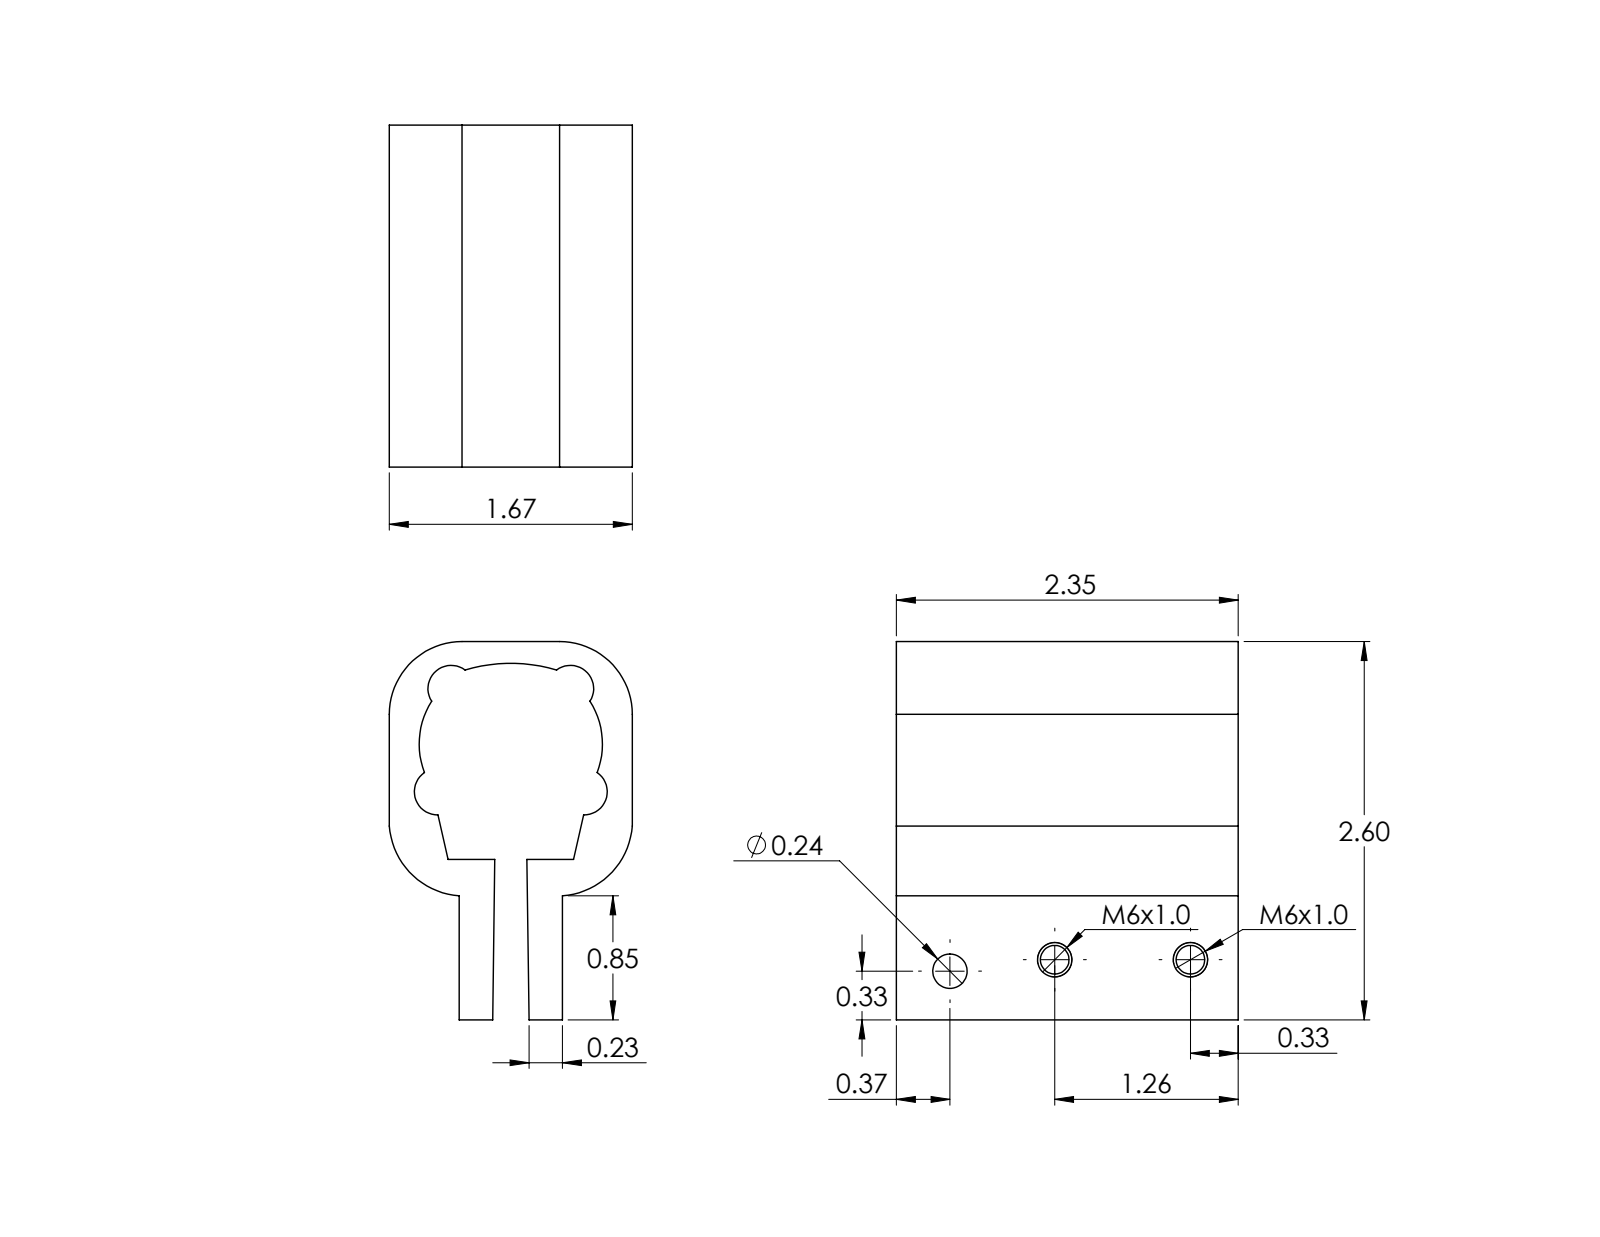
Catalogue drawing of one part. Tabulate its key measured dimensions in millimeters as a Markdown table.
| quantity | value |
| --- | --- |
| part name | BRK-10 |
| STEP written by | SolidWorks 2018 (AUTOMOTIVE_DESIGN) |
| units | millimeters |
| bodies | 1 solid, 41 faces (15 planar, 26 cylindrical, 0 other) |
| overall size | 66.04 × 59.69 × 42.42 |
| volume | 57 892 mm³ |
| surface area | 23 923 mm² |
| round holes (diameter × count) | 6 × 3, 5 × 2 |
| partial cylindrical surfaces (radius × count) | 4.06 × 4, 12.7 × 2, 13.19 × 2, 13.89 × 2, 28.4 × 1 |
| main face-to-face distances | 12.19, 30.22, 18.03, 42.41, 59.69, 38.04, 28, 66.04 |
| hole center spacings | 18.41, 23.7, 42.05 |
